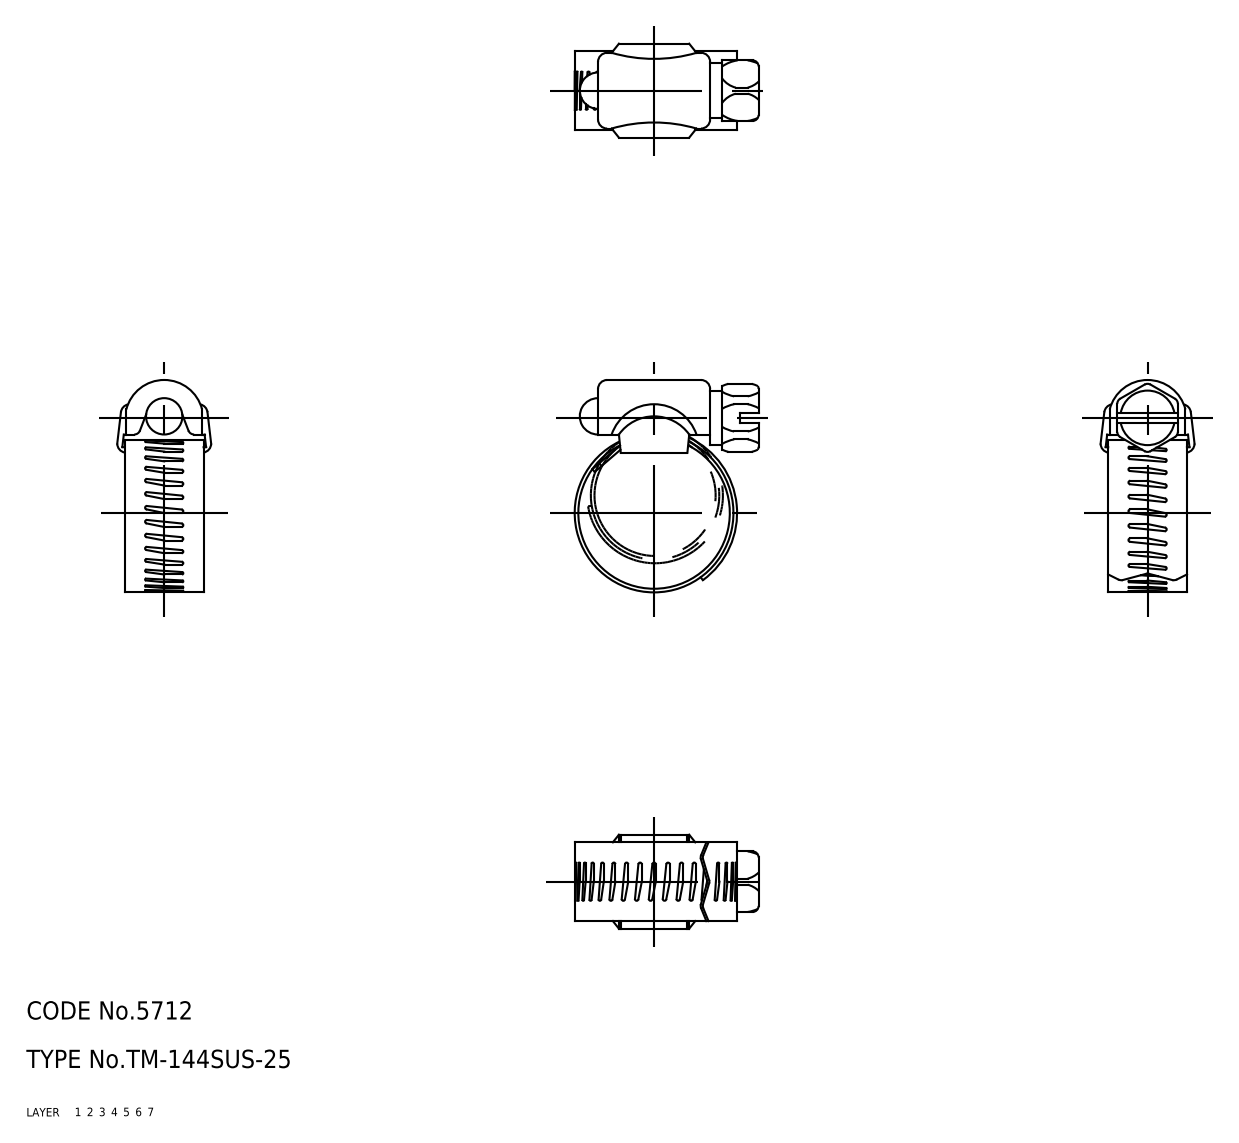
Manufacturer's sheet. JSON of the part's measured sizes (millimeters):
{"part_name": "band; screw; holder; TM_144SUS_25_20468_36", "step_written_by": "CADfix (AUTOMOTIVE_DESIGN)", "units": "millimeters", "bodies": {"solids": 3, "faces": 228, "planar": 0, "cylindrical": 0, "other": 228}, "overall_size": [35.18, 30.35, 15.63], "volume_mm3": 3170, "surface_area_mm2": 5580}
